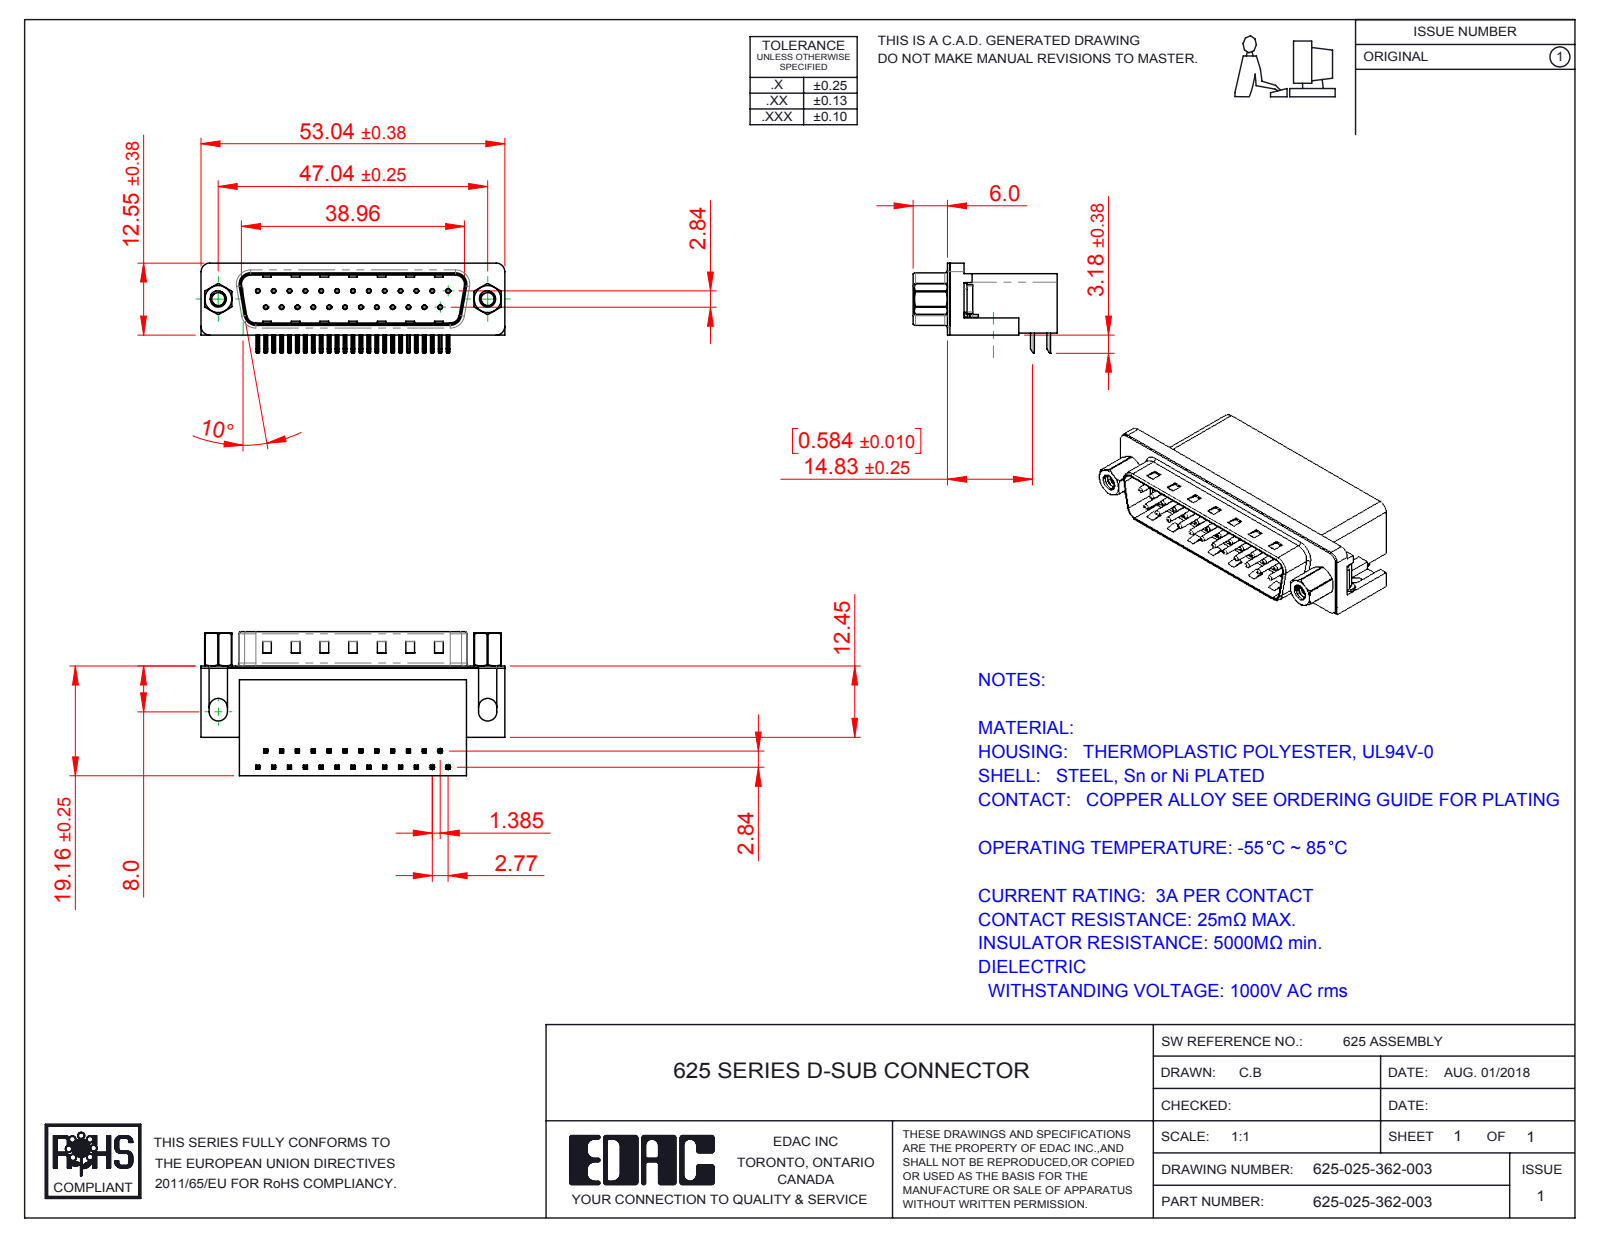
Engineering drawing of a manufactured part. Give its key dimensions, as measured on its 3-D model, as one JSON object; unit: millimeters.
{"part_name": "625 Shell_25 Socket; 625 4-40 Hex Standoff 5; 625 Housing_25 Socket; 625-025-362-003 (+4 more)", "step_written_by": "SolidWorks 2016 (CONFIG_CONTROL_DESIGN)", "units": "millimeters", "bodies": {"solids": 33, "faces": 2389, "planar": 1429, "cylindrical": 729, "other": 231}, "overall_size": [53.04, 25.16, 15.73], "volume_mm3": 9350, "surface_area_mm2": 9211, "round_holes": [[0.35, 25], [0.8, 25], [2.26, 2], [2.29, 2], [4, 2], [4.8, 2], [5, 2]], "round_bosses_or_shafts": [[0.75, 25], [4.9, 2], [4.75, 2], [3.9, 2], [2.79, 2]], "partial_cylinders_radius": [[0.25, 108], [0.12, 50], [1, 16], [0.5, 9], [1.6, 8], [1.5, 7], [0.9, 4], [2, 4]], "face_to_face_distances": [0.4, 10.35, 18.76, 2.1, 8.76, 10.46, 10.86, 1.7, 19.16, 10.11], "hole_center_spacings": [3.16, 2.77, 11.08, 5.54, 8.31, 5.03, 13.85, 7.48]}
